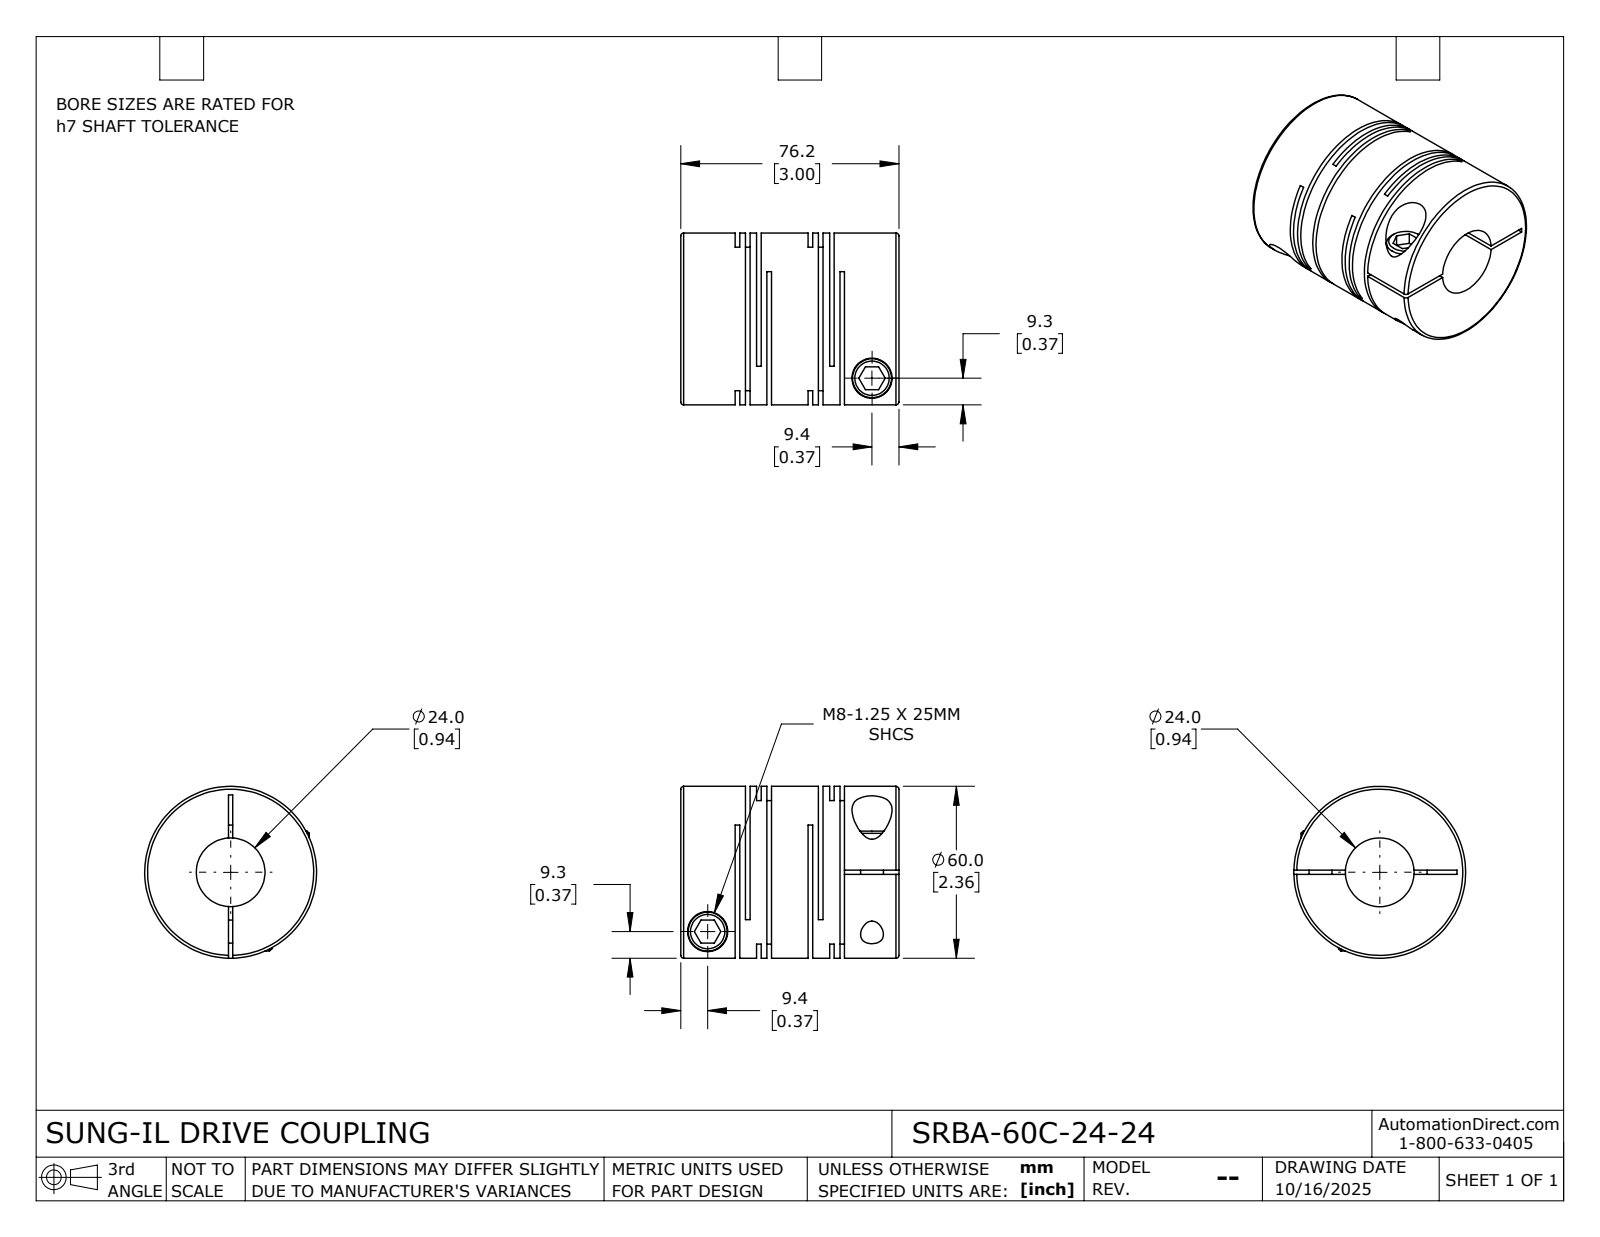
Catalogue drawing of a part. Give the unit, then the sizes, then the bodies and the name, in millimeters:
Units: millimetres
Overall size (bounding box): 76.2 × 60 × 60
Round holes (diameter × count): ⌀8 ×2, ⌀14 ×2, ⌀24 ×1
Round bosses / shafts (diameter × count): ⌀13.6 ×2, ⌀60 ×1
Main face-to-face distances: 1.6, 3.6, 7.5, 25.5, 33, 2, 5.9, 23.9, 3.9, 18
Volume: 151 742 mm³ · Surface area: 57 149 mm²
Bodies: 1 solid, 115 faces (60 planar, 42 cylindrical, 13 other)
Part name (STEP PRODUCT): SRBA-60C-24-24
STEP written by: SolidWorks 2024 (CONFIG_CONTROL_DESIGN)
